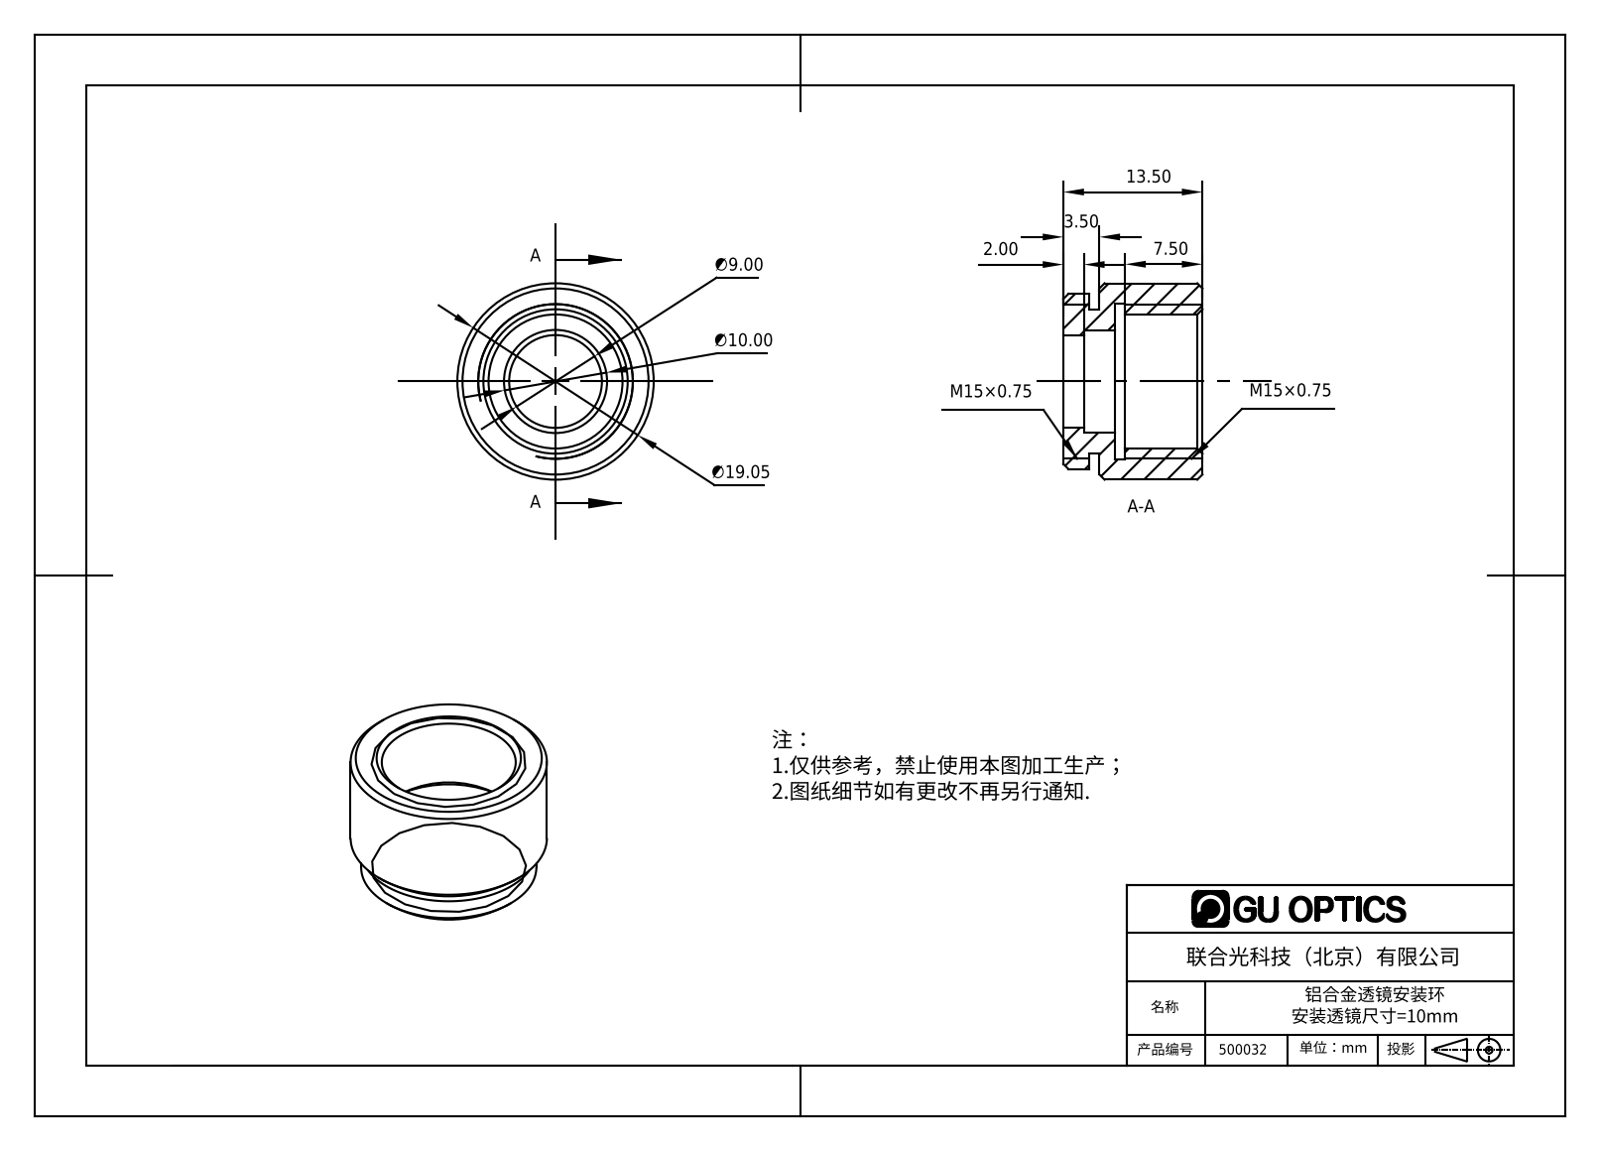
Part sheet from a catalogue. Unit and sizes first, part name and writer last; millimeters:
Units: millimetres
Overall size (bounding box): 19.05 × 19.05 × 13.5
Round holes (diameter × count): ⌀9 ×1, ⌀10 ×1, ⌀13 ×1, ⌀15.2 ×1
Round bosses / shafts (diameter × count): ⌀19.05 ×1, ⌀17 ×1, ⌀14 ×1
Main face-to-face distances: 2.5, 3.5, 1, 1.5, 5, 13.5, 10, 8.5, 11, 6
Volume: 2 005 mm³ · Surface area: 1 904 mm²
Bodies: 1 solid, 29 faces (7 planar, 14 cylindrical, 8 other)
Part name (STEP PRODUCT): 500032
STEP written by: SolidWorks 2016 (AUTOMOTIVE_DESIGN)
